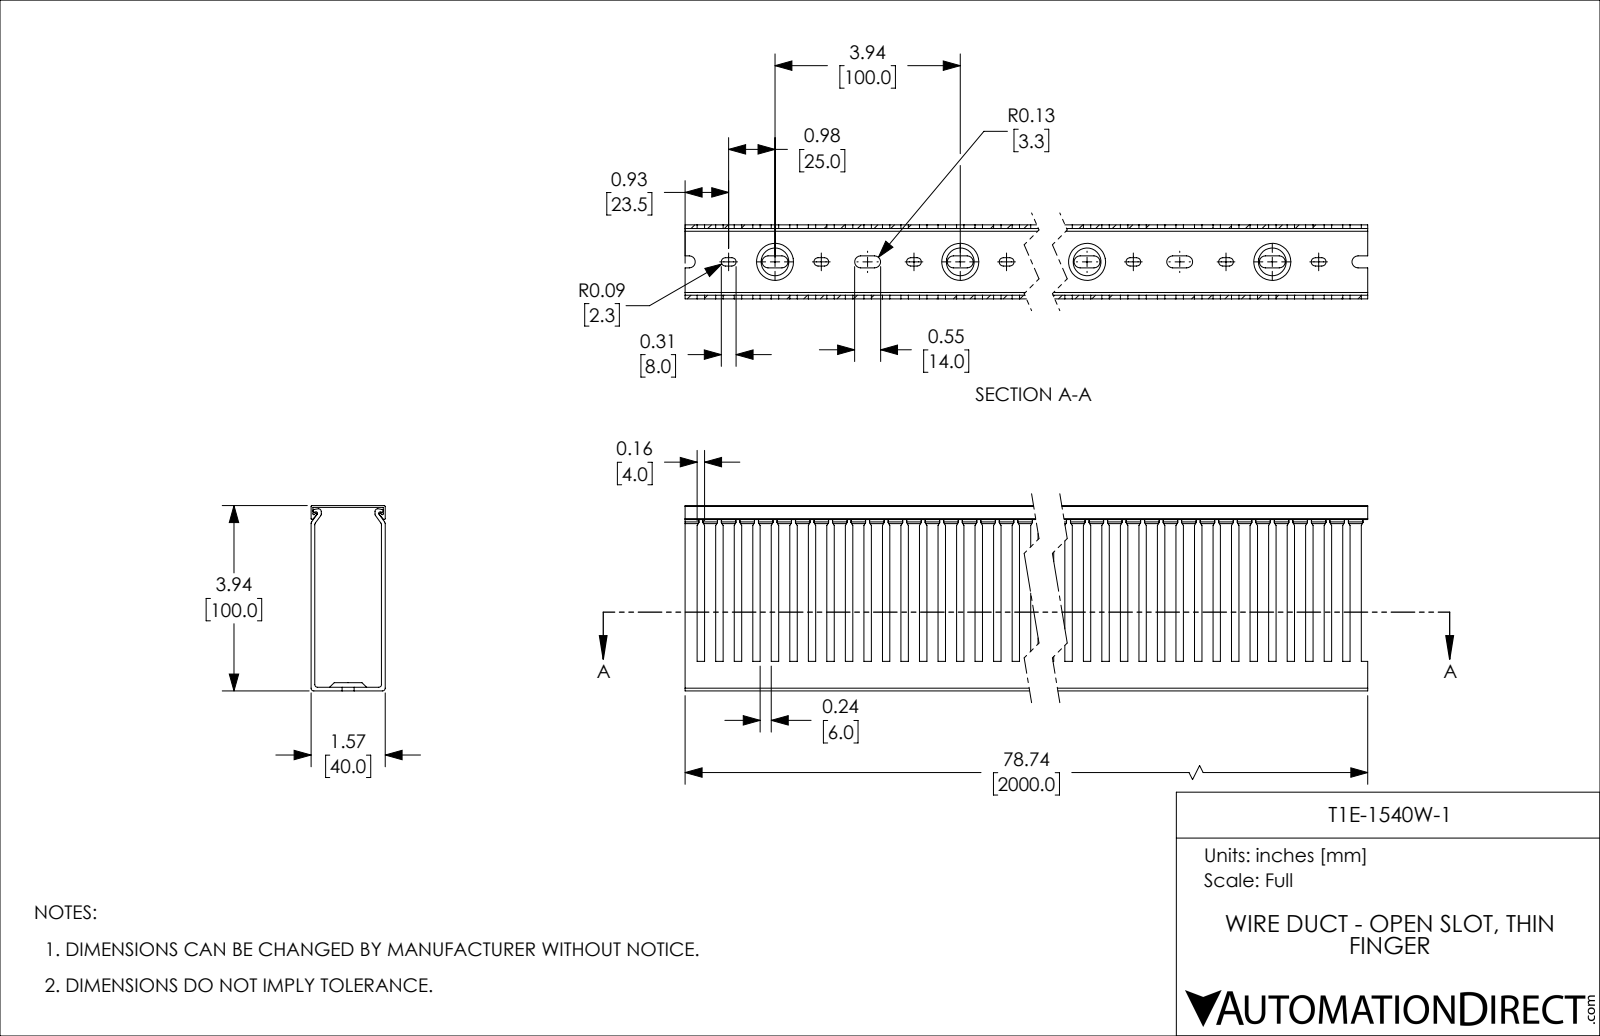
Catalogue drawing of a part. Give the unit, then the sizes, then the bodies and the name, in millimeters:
Units: millimetres
Overall size (bounding box): 2000 × 100 × 40
Partial cylindrical surfaces — rounded edges, fillets, slot ends (radius × count): R2.25 ×80, R3.25 ×80, R1.5 ×12, R0.5 ×8, R0.75 ×6
Main face-to-face distances: 2, 38, 40, 36, 1, 99, 100, 97, 98, 39
Volume: 1 056 000 mm³ · Surface area: 1 176 000 mm²
Bodies: 2 solids, 1005 faces (534 planar, 431 cylindrical, 40 other)
Part name (STEP PRODUCT): T1E-1540W-1
STEP written by: SolidWorks 2021 (CONFIG_CONTROL_DESIGN)
